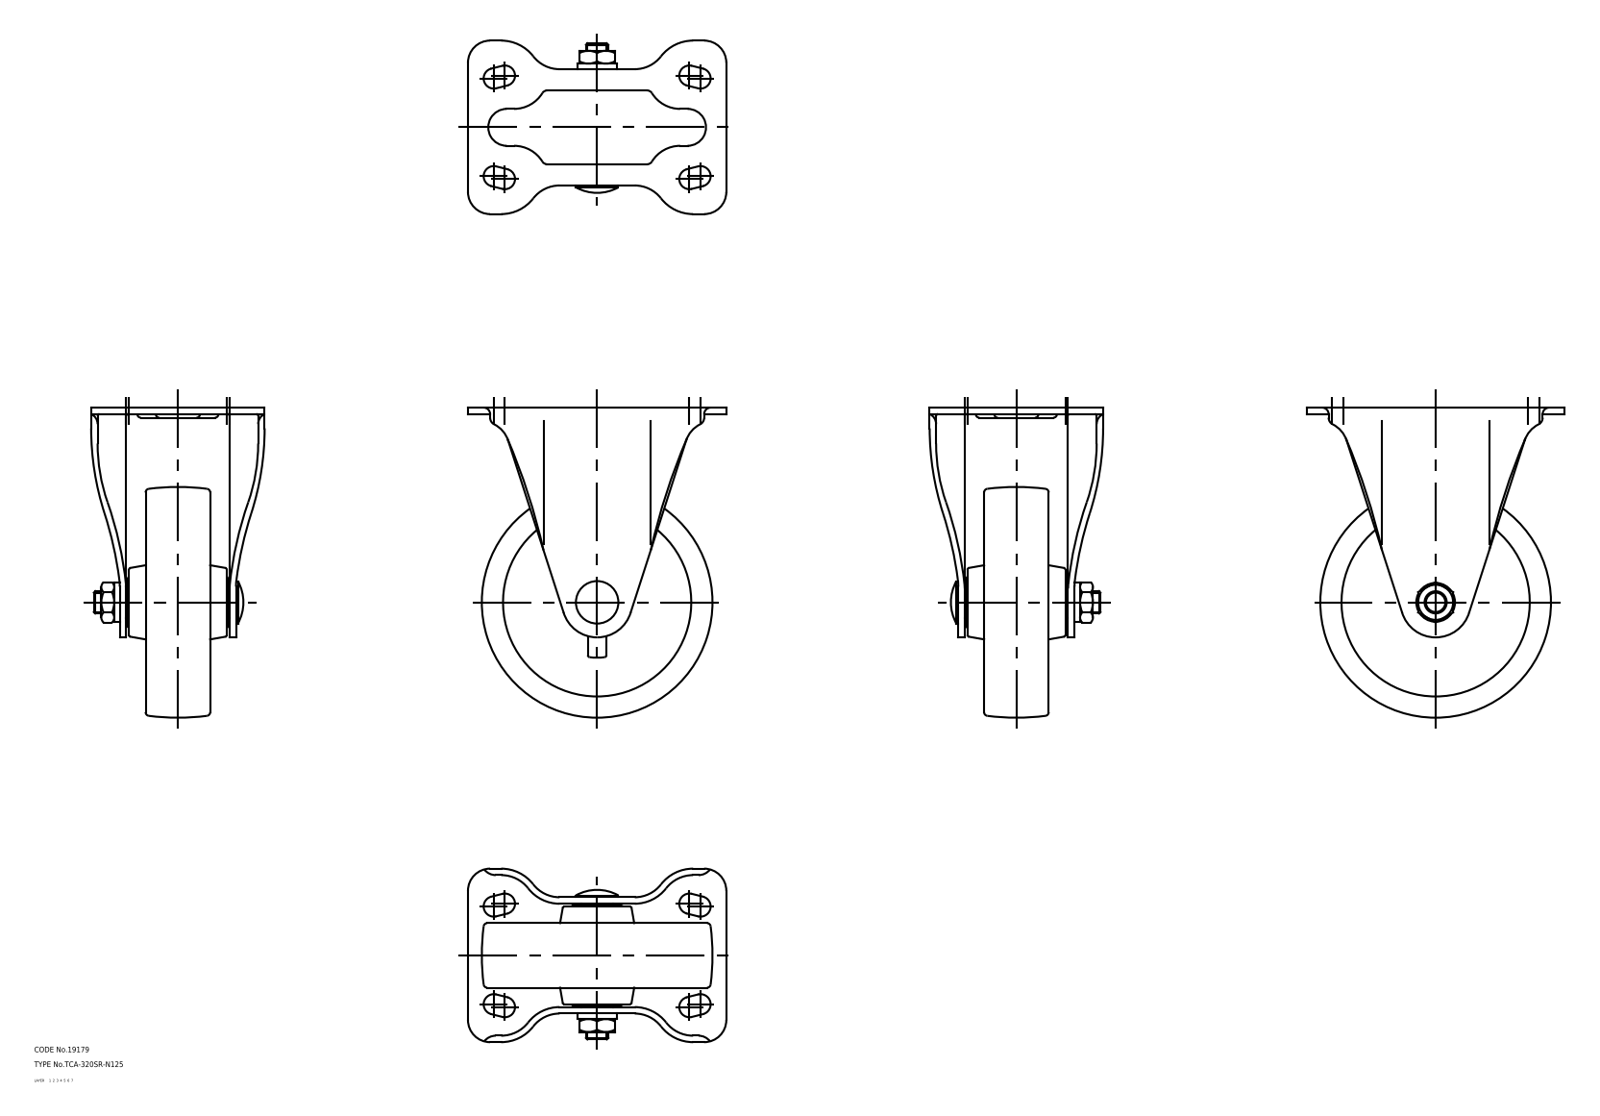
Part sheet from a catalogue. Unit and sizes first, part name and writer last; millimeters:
Units: millimetres
Overall size (bounding box): 168 × 140 × 94
Volume: 443 590 mm³ · Surface area: 110 020 mm²
Bodies: 3 solids, 231 faces (0 planar, 0 cylindrical, 231 other)
Part name (STEP PRODUCT): 67123181; 67123194; 67123207
STEP written by: CADfix (AUTOMOTIVE_DESIGN)
